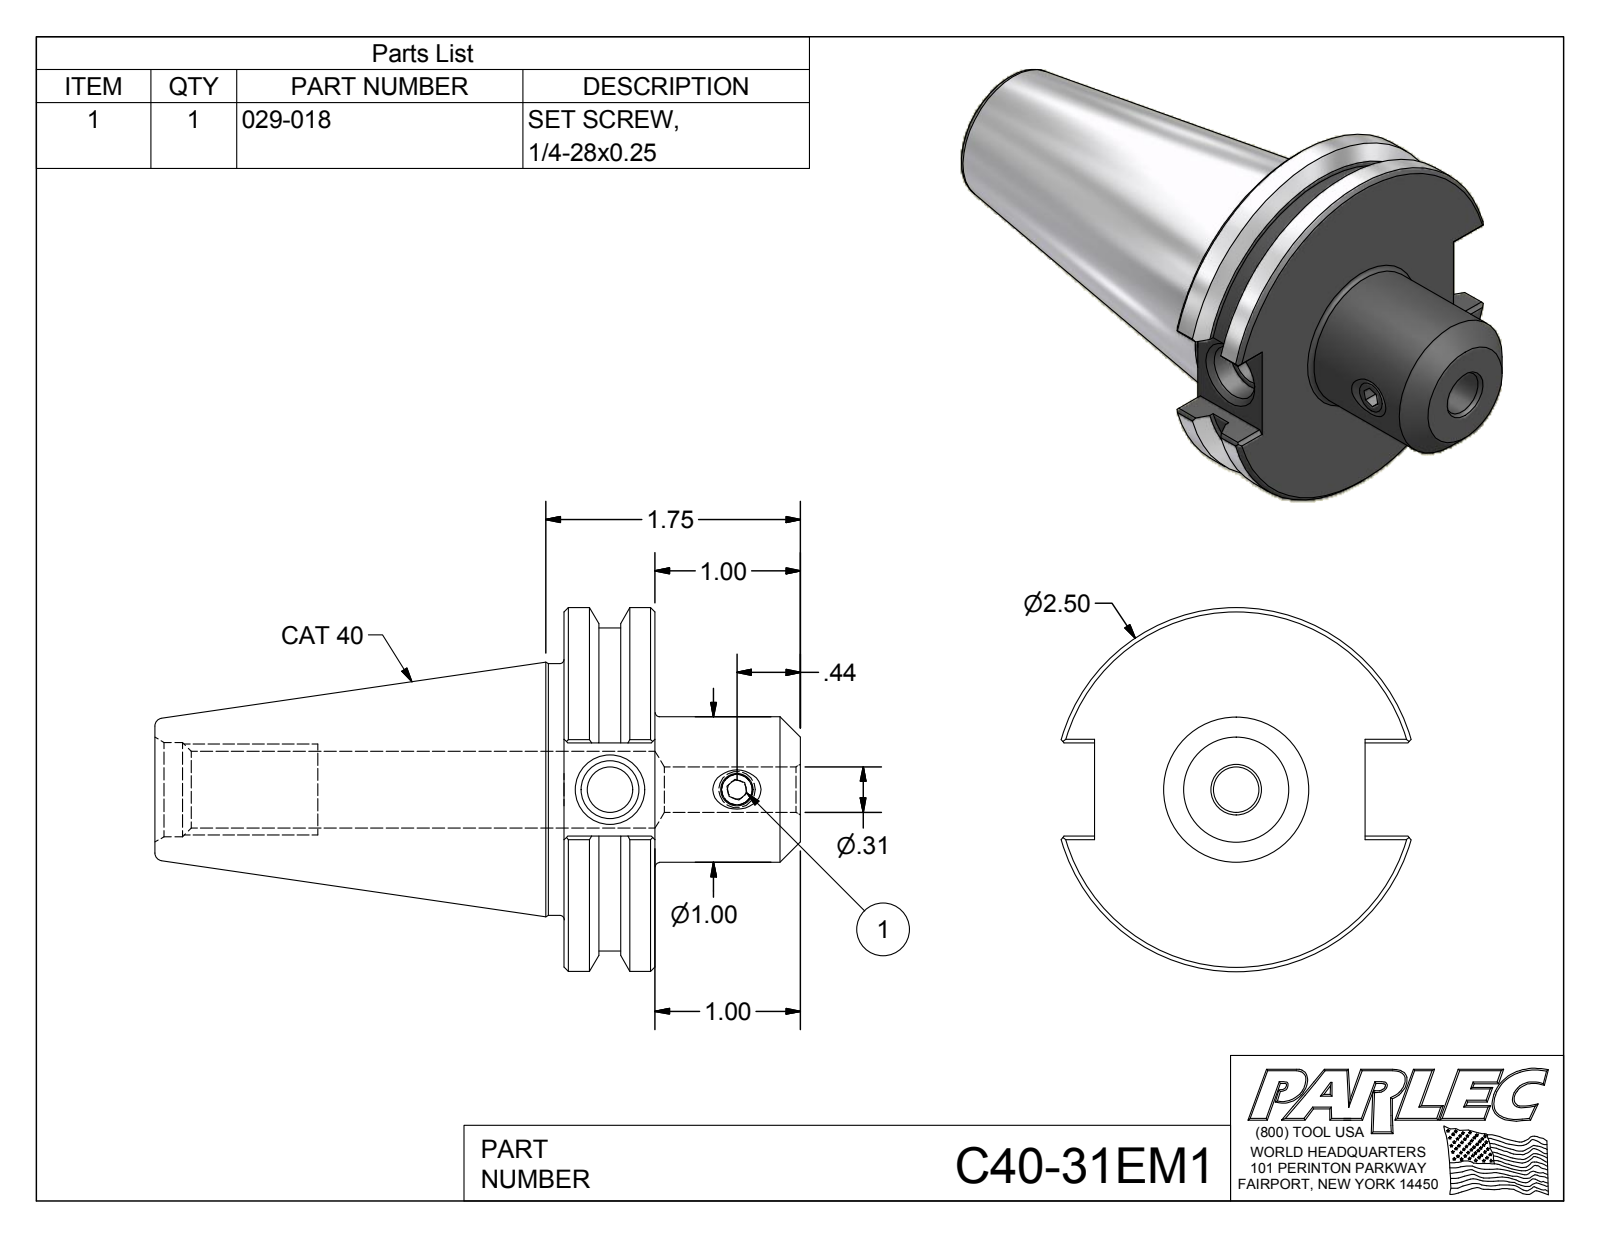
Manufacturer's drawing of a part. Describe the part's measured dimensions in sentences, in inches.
The part is named "C40-31EM1; C40-31EM1-1; 029-018". Its 3-D file was written by "Autodesk Inventor 2012 (AUTOMOTIVE_DESIGN)". It is 2 solids with 79 faces: 40 planar, 16 cylindrical and 23 other. Overall it measures 4.438 by 2.5 by 2.403 inches. Its volume is 6.79 cubic inches and its surface area 35.96 square inches. Round holes: 1 of diameter 0.209, 1 of diameter 0.211, 1 of diameter 0.313, 1 of diameter 0.315, 1 of diameter 0.396, 1 of diameter 0.527, 1 of diameter 0.648. Round bosses or shafts: 1 of diameter 2.5, 1 of diameter 2.219, 1 of diameter 1.73, 1 of diameter 1, 1 of diameter 0.25. The main face-to-face distances are 0.625, 1.625, 1, 0.64, 1.86, 2.813, 3.437, 4.437, 3.201, 0.389. The hole center spacings are 0.873.
